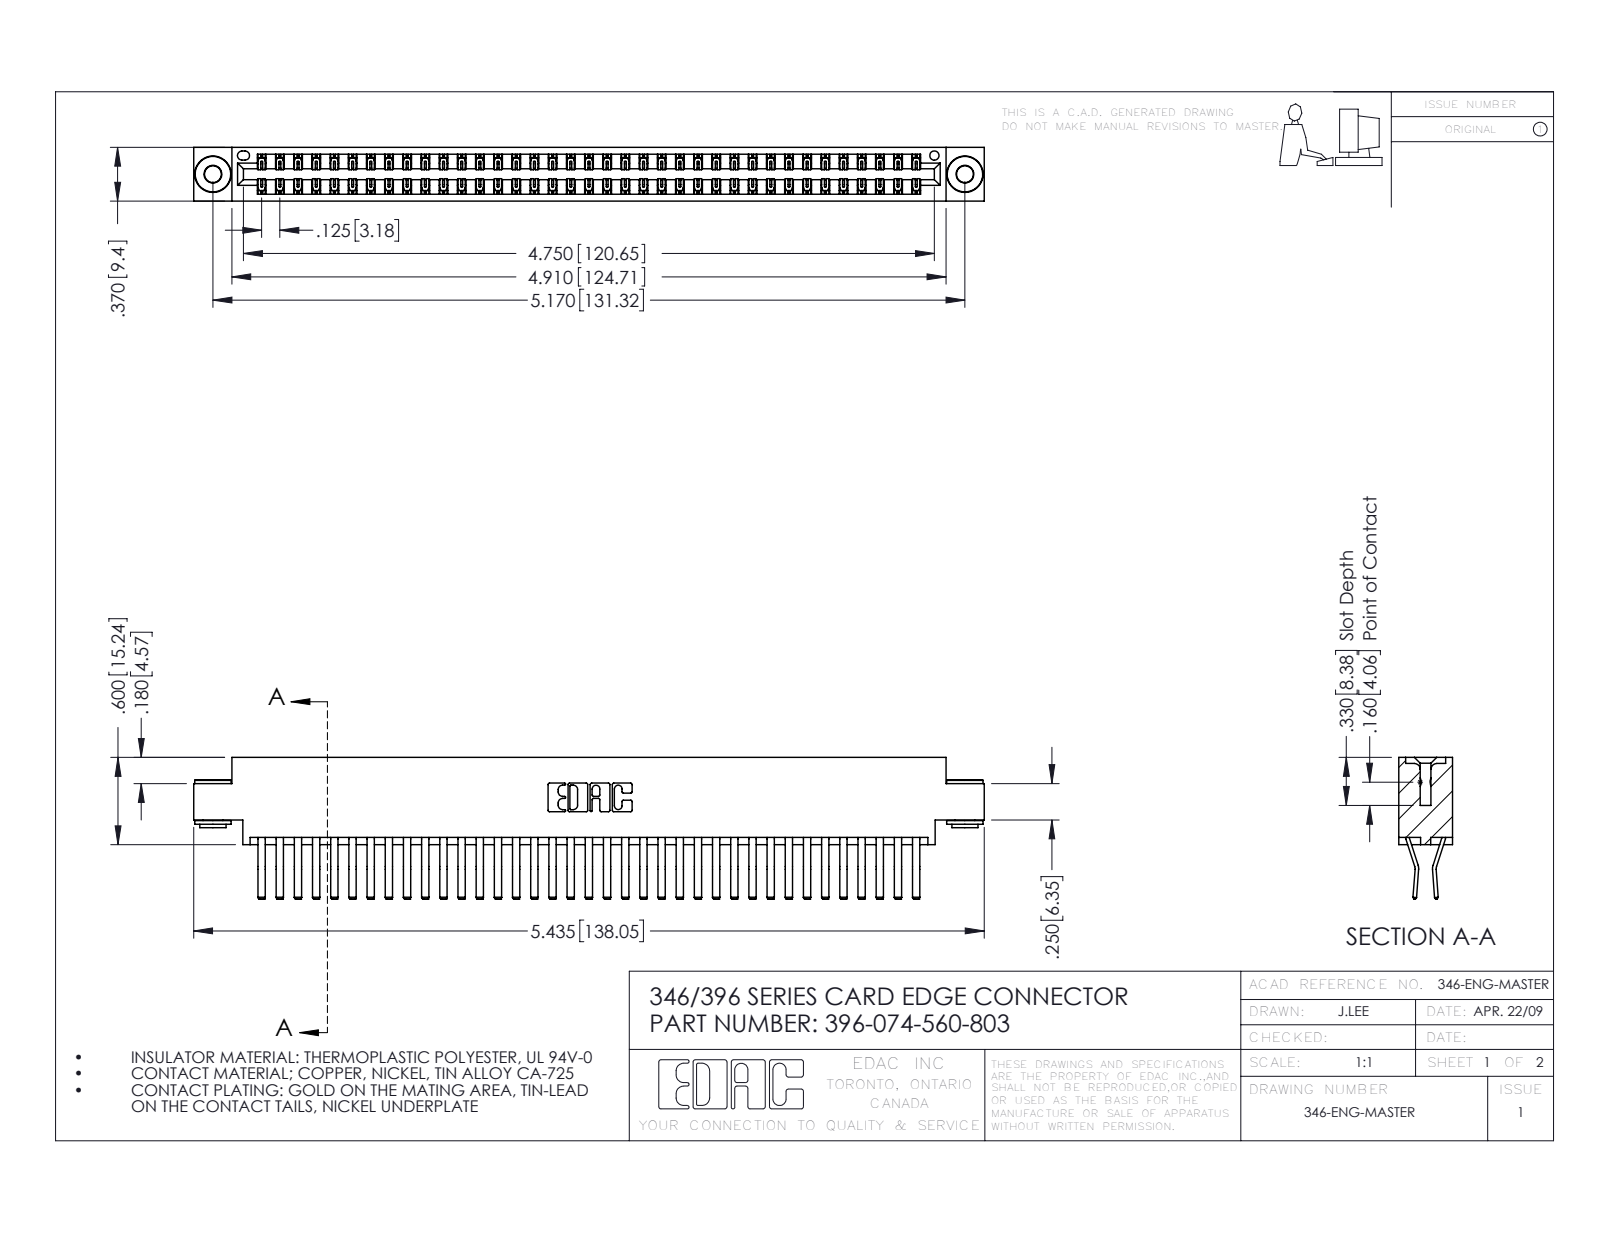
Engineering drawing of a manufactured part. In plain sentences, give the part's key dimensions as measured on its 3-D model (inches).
The part is named "396-074-560-803; 345-250-002_345-250-002-102; 346 Part_0.170 Offset - 0.156 Dia-TH; 345-292-001_560 Tail". Its 3-D file was written by "SolidWorks 2016 (CONFIG_CONTROL_DESIGN)". It is 77 solids with 4160 faces: 2680 planar, 1472 cylindrical and 8 other. Overall it measures 5.435 by 0.975 by 0.37 inches. Its volume is 0.84 cubic inches and its surface area 31.84 square inches. Round holes: 2 of diameter 0.116, 2 of diameter 0.156, 1 of diameter 0.064. Round bosses or shafts: 2 of diameter 0.25, 2 of diameter 0.18, 2 of diameter 0.136. Partial cylindrical surfaces (rounded edges, fillets, slot ends): 111 of radius 0.006, 22 of radius 0.01, 6 of radius 0.007, 6 of radius 0.031, 3 of radius 0.026, 2 of radius 0.01, 2 of radius 0.014, 2 of radius 0.022. The main face-to-face distances are 0.048, 0.322, 0.37, 0.025, 0.25, 0.275, 0.072, 0.298, 0.148, 0.222. The hole center spacings are 0.246, 4.961, 5.17.
